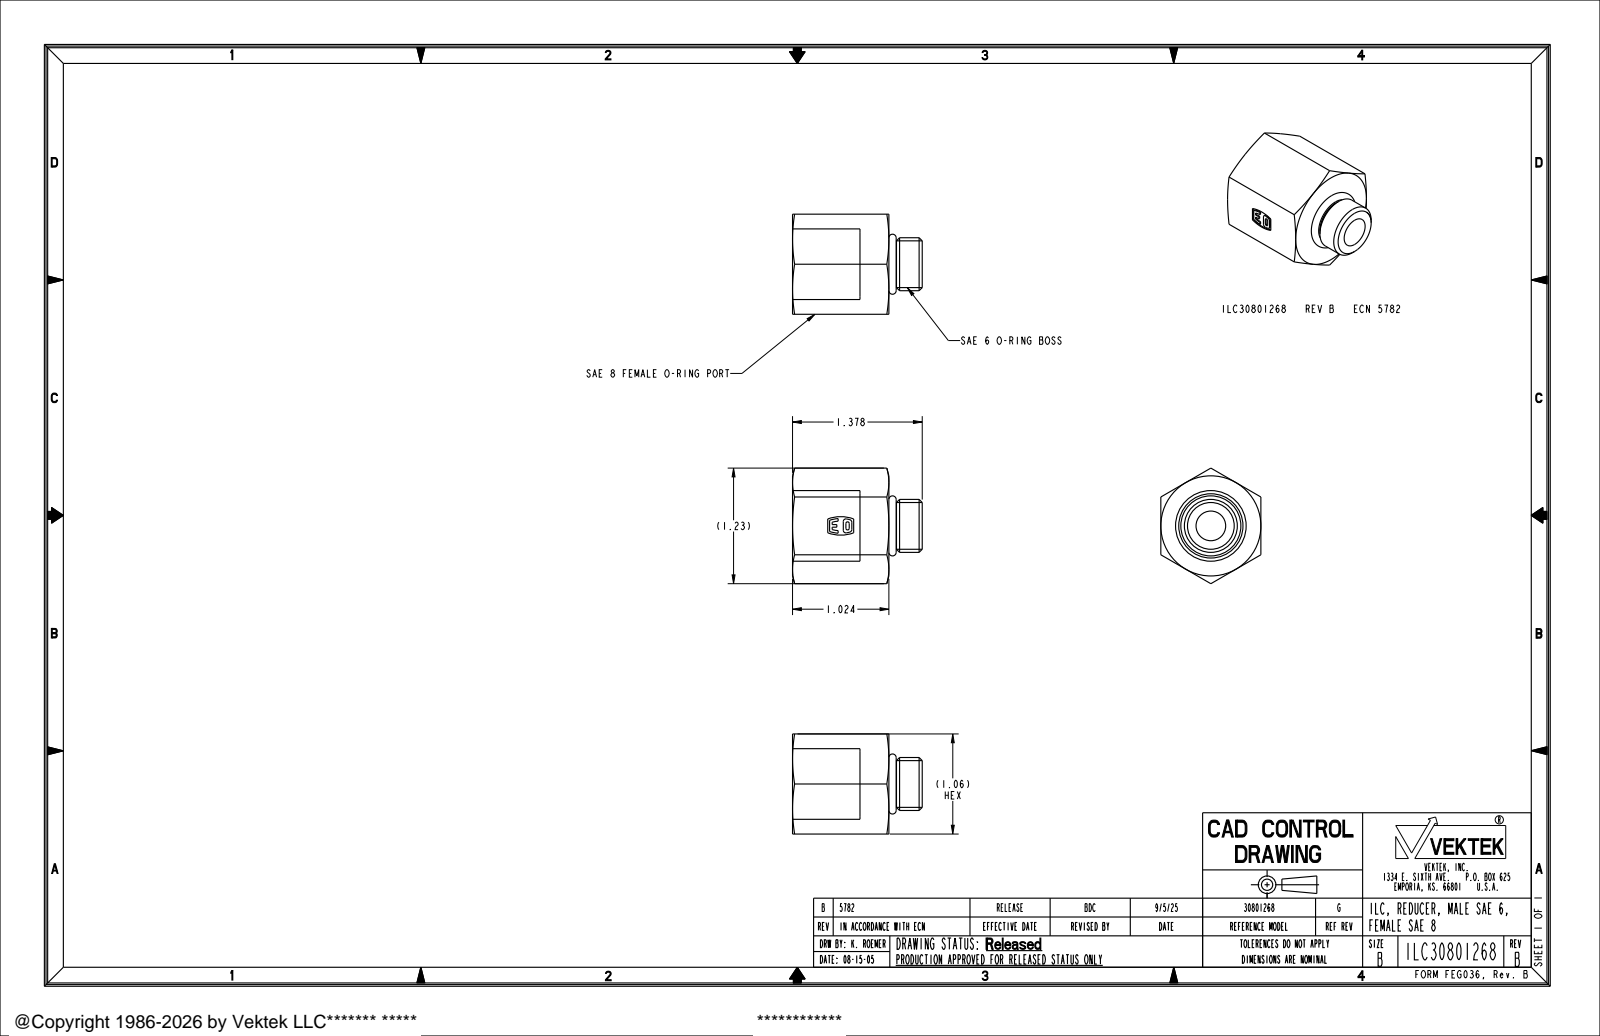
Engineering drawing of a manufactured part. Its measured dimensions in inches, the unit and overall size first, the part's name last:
Units: inches
Overall size (bounding box): 1.37 × 1.227 × 1.063
Round holes (diameter × count): ⌀0.3 ×1, ⌀0.75 ×1
Round bosses / shafts (diameter × count): ⌀0.563 ×1
Main face-to-face distances: 1.062, 0.885, 0.68, 0.205, 0.985, 0.305, 0.1, 1.37, 0.69, 0.485
Volume: 0.66 in³ · Surface area: 8.264 in²
Bodies: 1 solid, 44 faces (12 planar, 10 cylindrical, 22 other)
Part name (STEP PRODUCT): ILC30801268
STEP written by: CREO PARAMETRIC BY PTC INC, 2021164 (AUTOMOTIVE_DESIGN)
